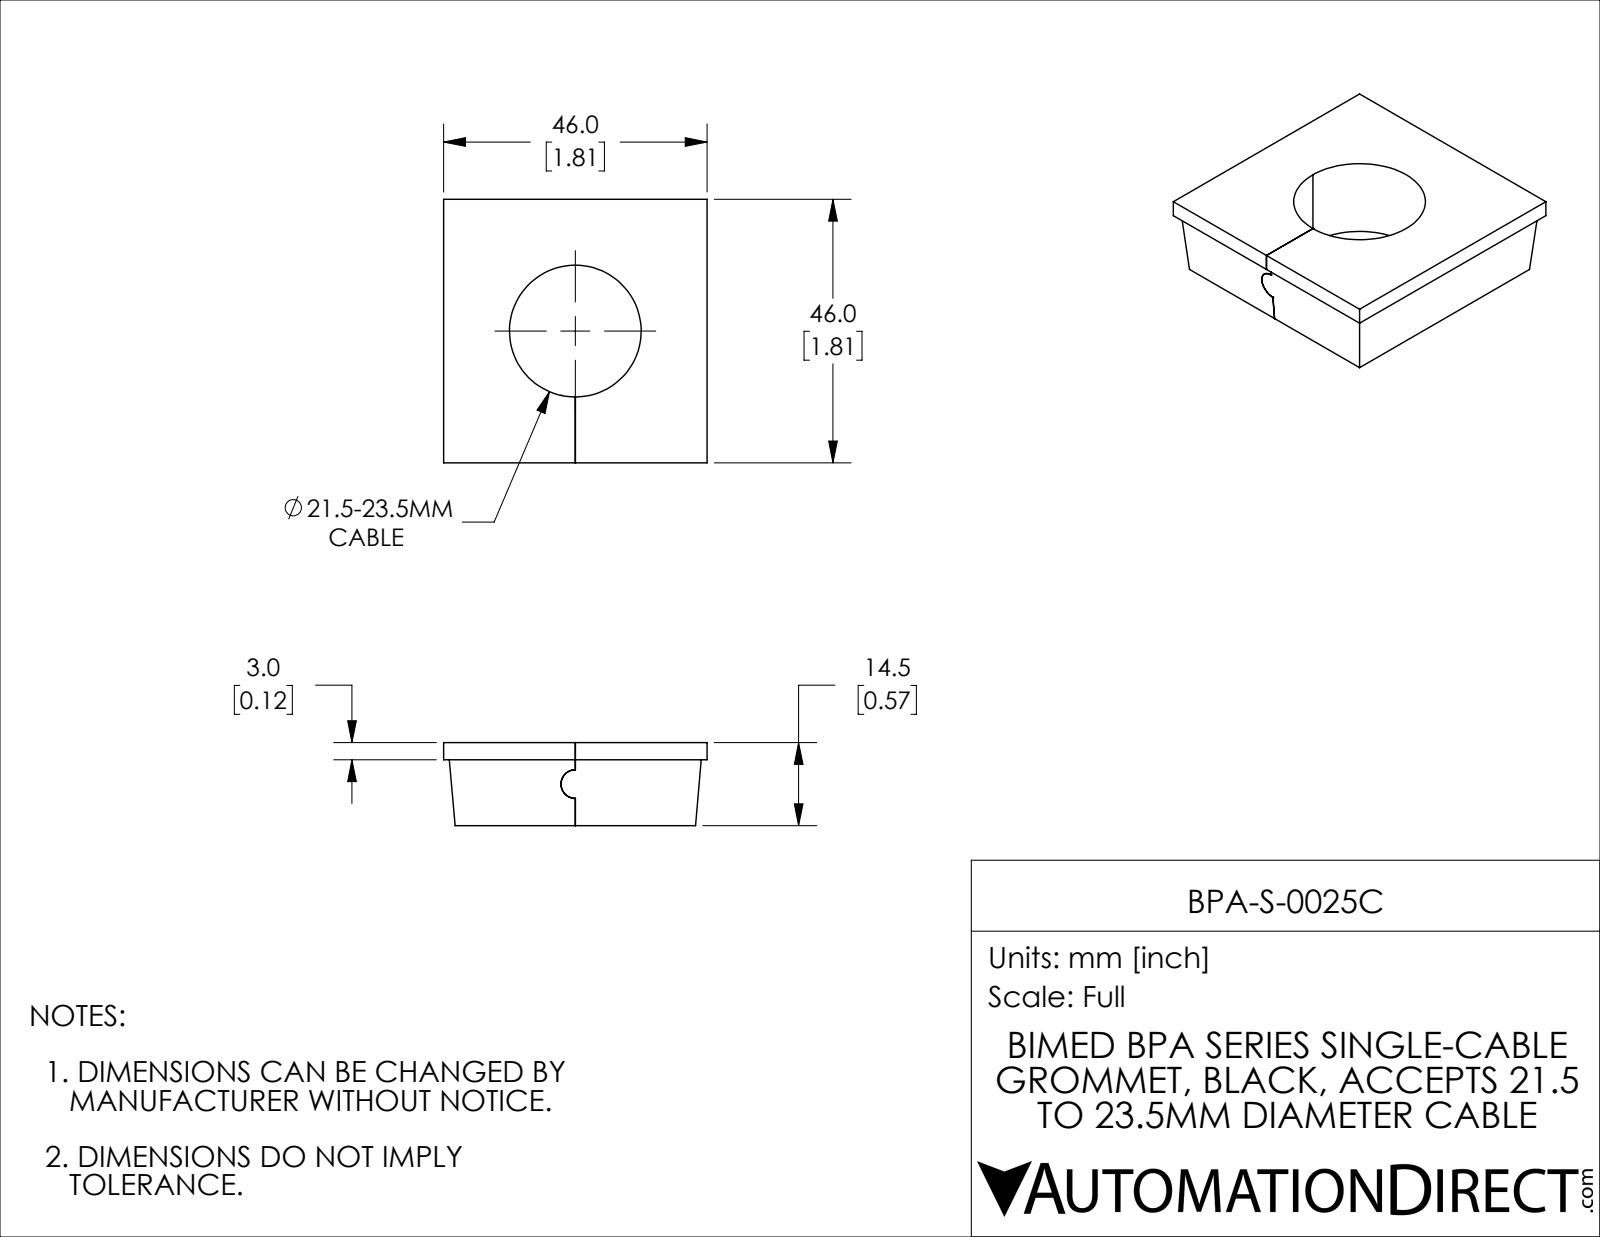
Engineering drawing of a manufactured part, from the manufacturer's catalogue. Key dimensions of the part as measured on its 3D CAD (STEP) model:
Part name (STEP PRODUCT): BPA-S-0025C
STEP written by: SolidWorks 2021 (CONFIG_CONTROL_DESIGN)
Units: millimetres
Bodies: 1 solid, 22 faces (17 planar, 5 cylindrical, 0 other)
Overall size (bounding box): 46 × 46 × 14.5
Volume: 21 583 mm³ · Surface area: 7 171 mm²
Round holes (diameter × count): ⌀23 ×1
Partial cylindrical surfaces — rounded edges, fillets, slot ends (radius × count): R2.5 ×1, R2.51 ×1
Main face-to-face distances: 14.5, 46, 22.99, 23.01, 11.5, 3
